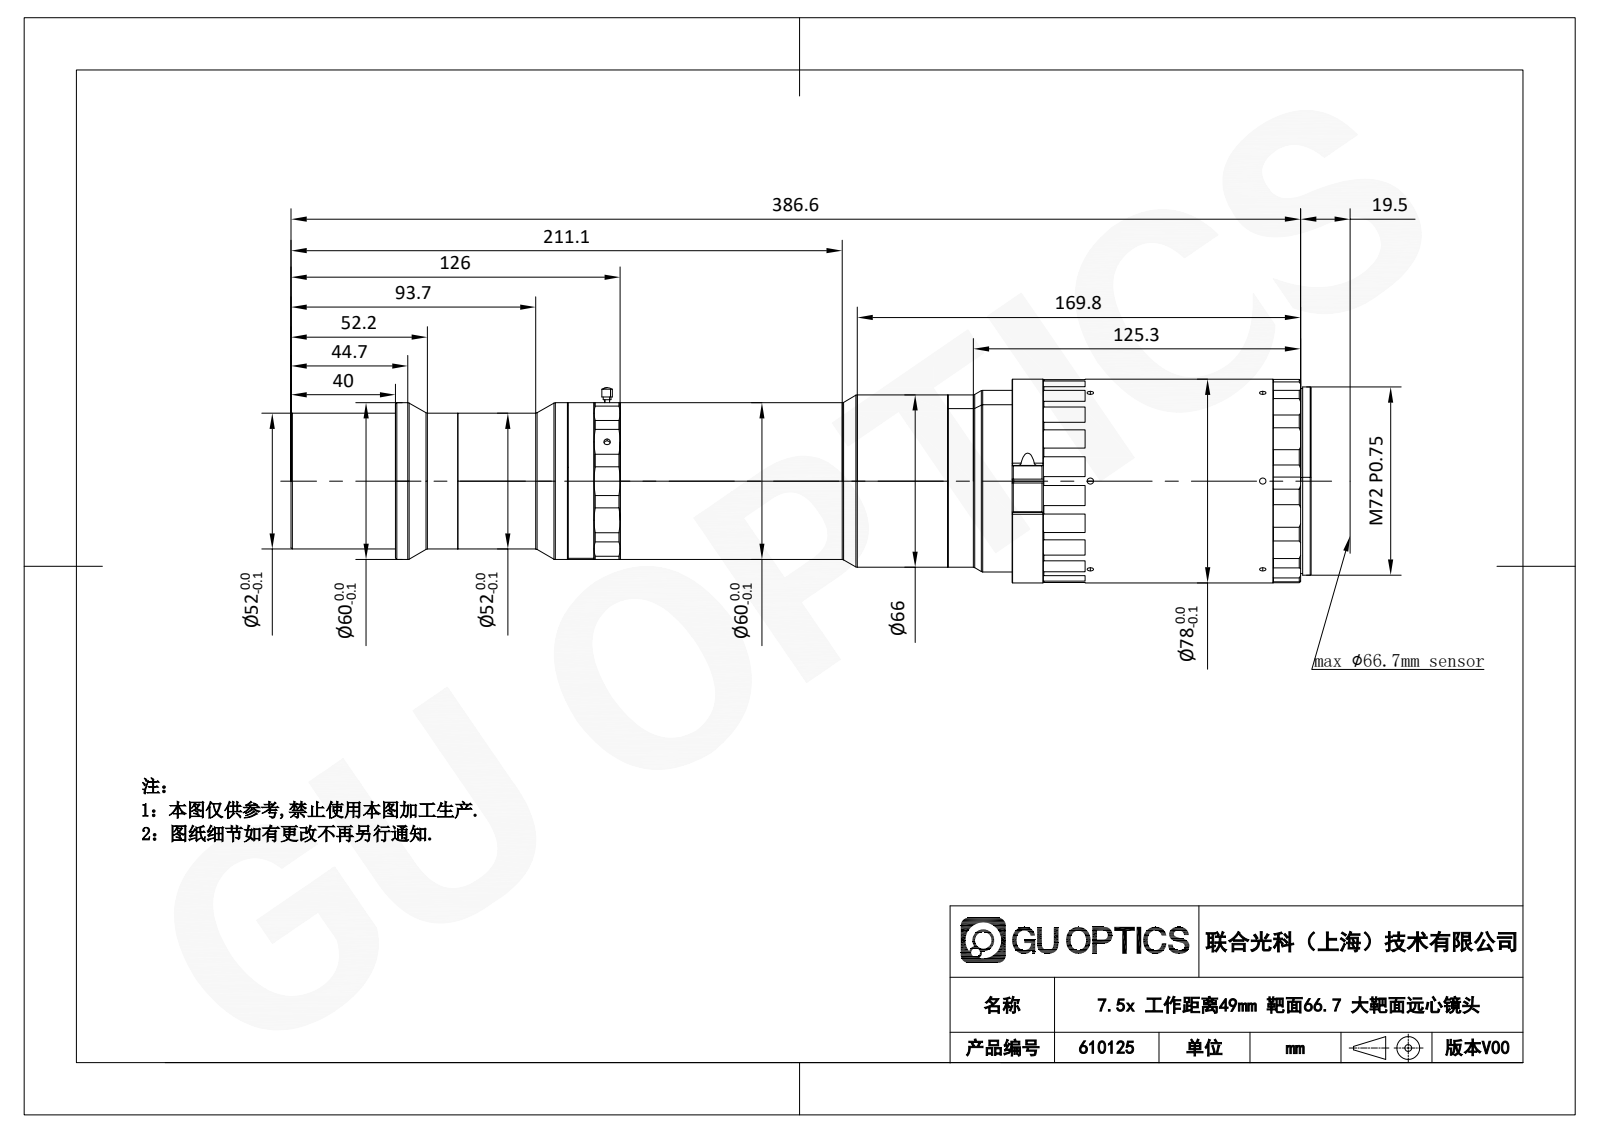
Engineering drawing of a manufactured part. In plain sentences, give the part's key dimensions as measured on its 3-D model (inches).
The part is named "DTCA150M-8.9-G-M72-19.5-AL". Its 3-D file was written by "SolidWorks 2017 (CONFIG_CONTROL_DESIGN)". It is 1 solid with 474 faces: 122 planar, 165 cylindrical and 187 other. Overall it measures 15.377 by 3.326 by 3.071 inches. Its volume is 75.06 cubic inches and its surface area 149.9 square inches. Round holes: 6 of diameter 0.094, 3 of diameter 0.098, 1 of diameter 0.087, 1 of diameter 0.134, 1 of diameter 0.177, 1 of diameter 1.831, 1 of diameter 2.539, 1 of diameter 2.657, 1 of diameter 2.795, 1 of diameter 2.925. Round bosses or shafts: 1 of diameter 3.071, 1 of diameter 2.913, 1 of diameter 2.835, 1 of diameter 2.787, 1 of diameter 2.736, 1 of diameter 2.598, 1 of diameter 2.362, 1 of diameter 2.047. Partial cylindrical surfaces (rounded edges, fillets, slot ends): 38 of radius 0.591, 2 of radius 0.039, 1 of radius 0.157, 1 of radius 1.201, 1 of radius 1.791. The main face-to-face distances are 3.7, 4.35, 0.651, 2.362, 9.294, 12.994, 13.644, 13.802, 4.508, 0.808. The hole center spacings are 2.598, 6.548.
